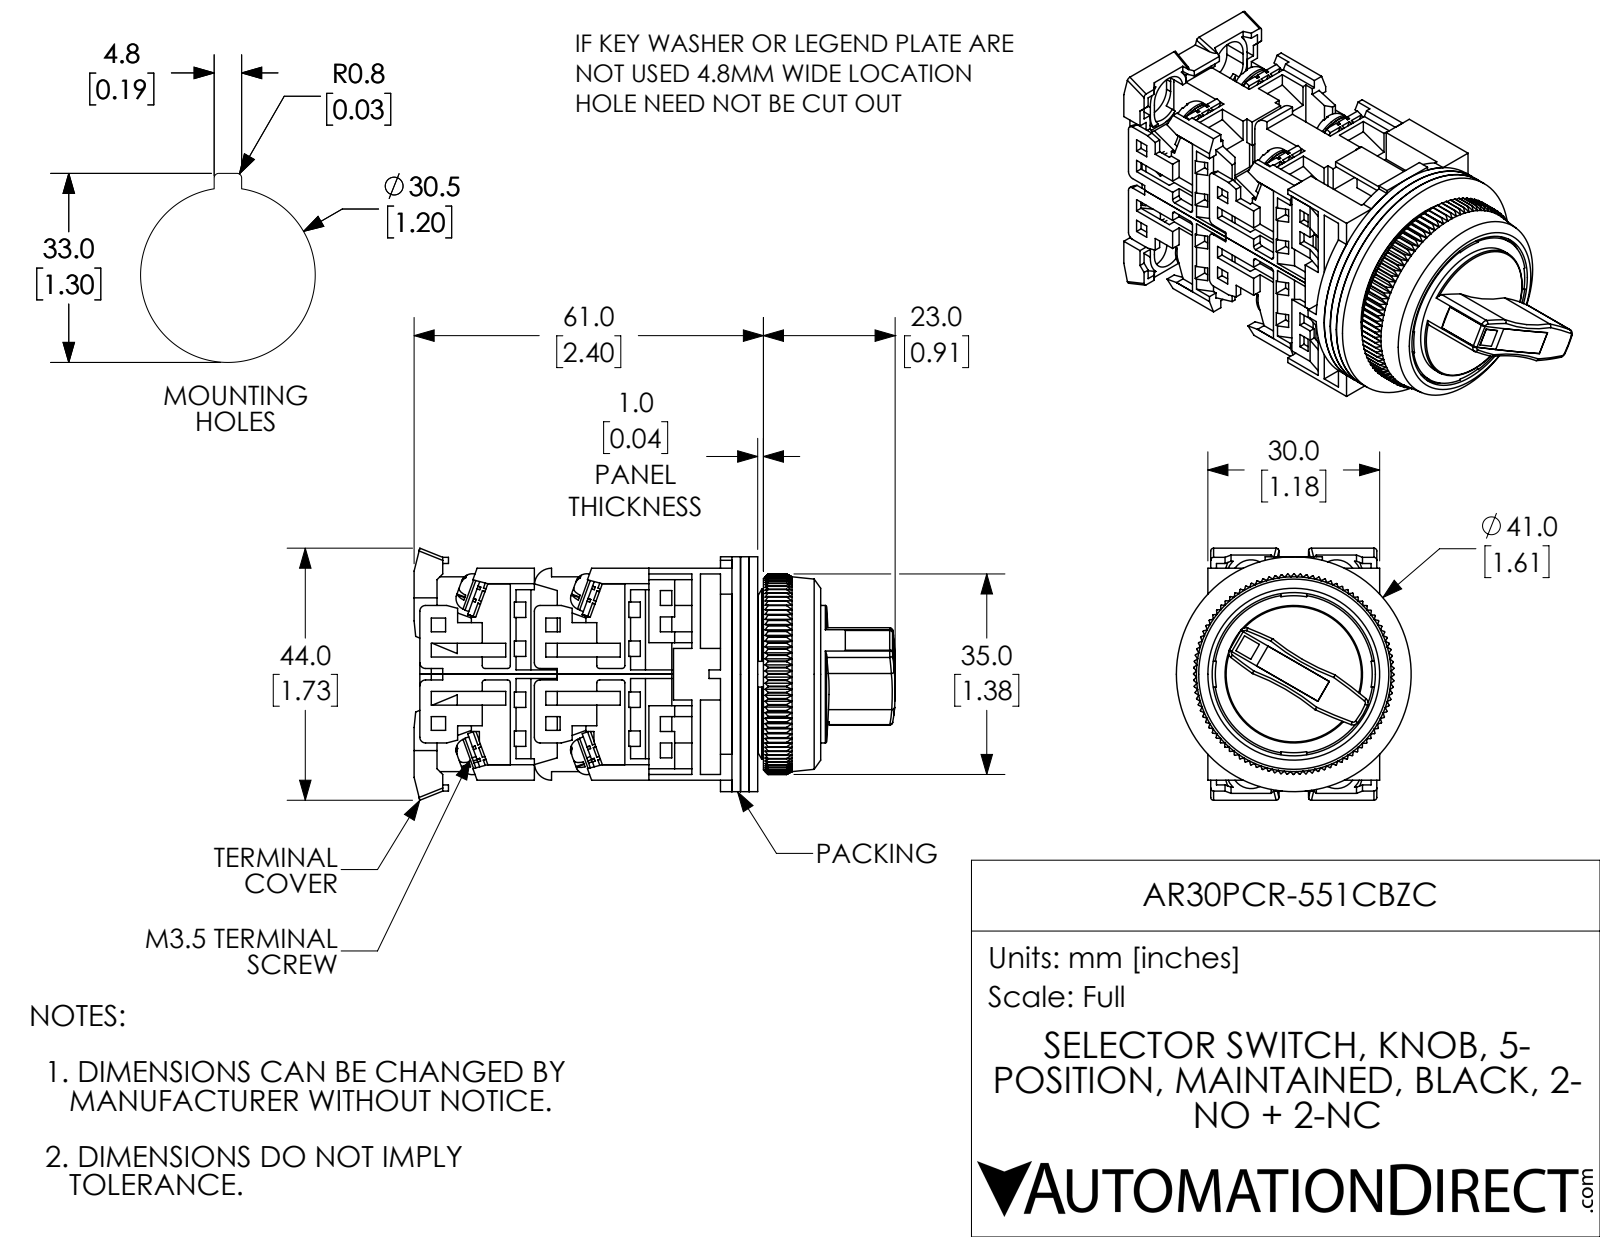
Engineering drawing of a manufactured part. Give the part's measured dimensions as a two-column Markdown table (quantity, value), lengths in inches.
| quantity | value |
| --- | --- |
| part name | AR30PCR-551CBZC |
| STEP written by | SolidWorks 2017 (AUTOMOTIVE_DESIGN) |
| units | inches |
| bodies | 39 solids, 2466 faces (1837 planar, 386 cylindrical, 243 other) |
| overall size | 3.307 × 1.732 × 1.614 |
| volume | 3.149 in³ |
| surface area | 74.85 in² |
| round holes (diameter × count) | 0.138 × 16, 0.142 × 8, 0.118 × 1, 0.315 × 1, 0.472 × 1, 0.48 × 1, 0.512 × 1, 0.819 × 1, 0.945 × 1, 1.122 × 1, 1.252 × 1 |
| round bosses / shafts (diameter × count) | 0.26 × 8, 0.138 × 8, 1.614 × 1, 1.181 × 1, 0.787 × 1, 0.709 × 1, 0.669 × 1, 0.559 × 1 |
| partial cylindrical surfaces (radius × count) | 0.059 × 32, 0.02 × 17, 0.039 × 12, 0.118 × 4, 0.138 × 4, 0.177 × 4, 1.575 × 2, 1.638 × 2 |
| main face-to-face distances | 0.059, 0.039, 0.118, 0.063, 0.787, 0.02, 0.689, 0.091, 0.067, 0.028 |
| hole center spacings | 0.579, 0.638, 0.269, 0.269, 0.61 |
